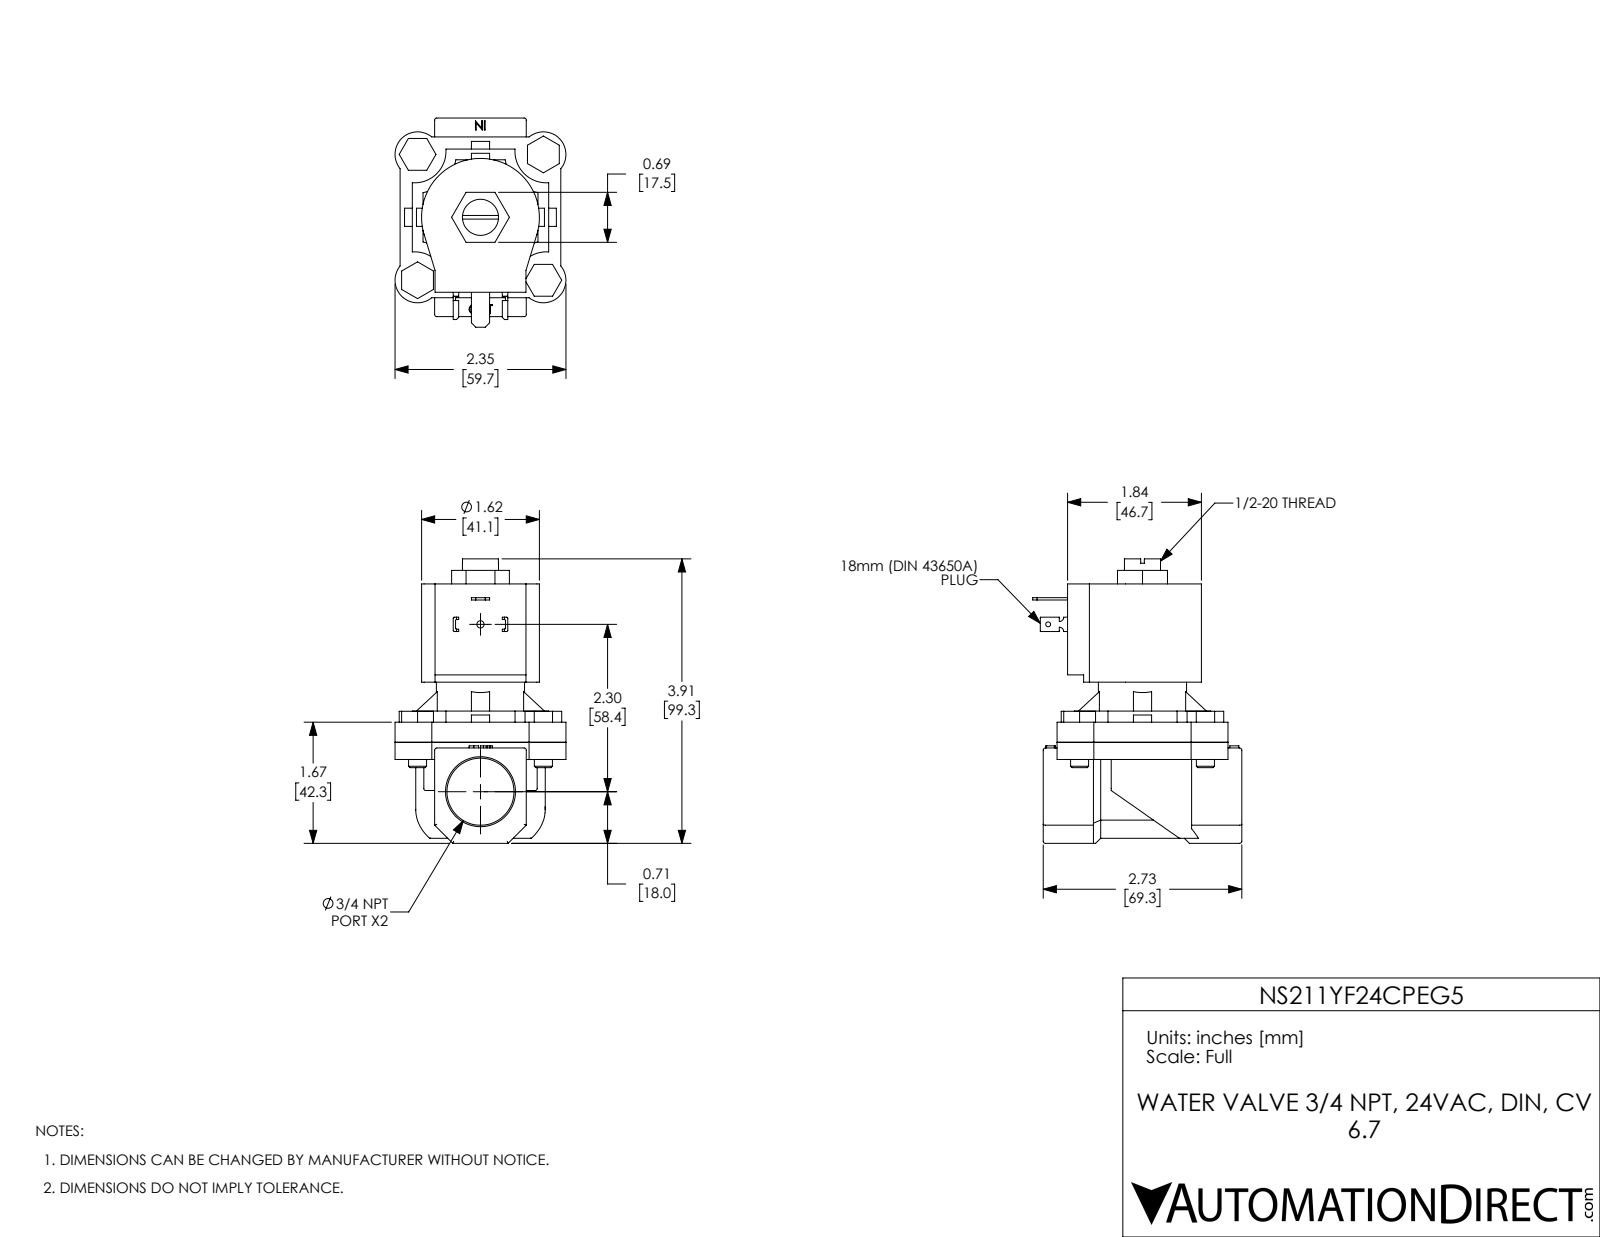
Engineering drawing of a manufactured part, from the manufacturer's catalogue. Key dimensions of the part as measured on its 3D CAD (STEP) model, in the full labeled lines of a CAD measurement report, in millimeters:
Part name (STEP PRODUCT): NS211YF24CPEG5
STEP written by: SolidWorks 2021 (CONFIG_CONTROL_DESIGN)
Units: millimetres
Bodies: 11 solids, 387 faces (241 planar, 113 cylindrical, 33 other)
Overall size (bounding box): 99.3 × 73 × 59.7
Volume: 163 800 mm³ · Surface area: 44 100 mm²
Round holes (diameter × count): ⌀6.4 ×4, ⌀1.7 ×1, ⌀2.5 ×1, ⌀12.6 ×1, ⌀13 ×1, ⌀23.4 ×1, ⌀29.3 ×1
Round bosses / shafts (diameter × count): ⌀6.3 ×4, ⌀30.8 ×1
Partial cylindrical surfaces — rounded edges, fillets, slot ends (radius × count): R0.8 ×15, R0.4 ×8, R7.9 ×4, R11 ×4, R14.7 ×4, R1.5 ×2, R20.6 ×1, R22.6 ×1
Main face-to-face distances: 7, 55.3, 48.3, 6, 13, 61.3, 27, 21, 14, 34.3
Hole centre spacings: 31.1, 43.9, 62.1, 58.4
